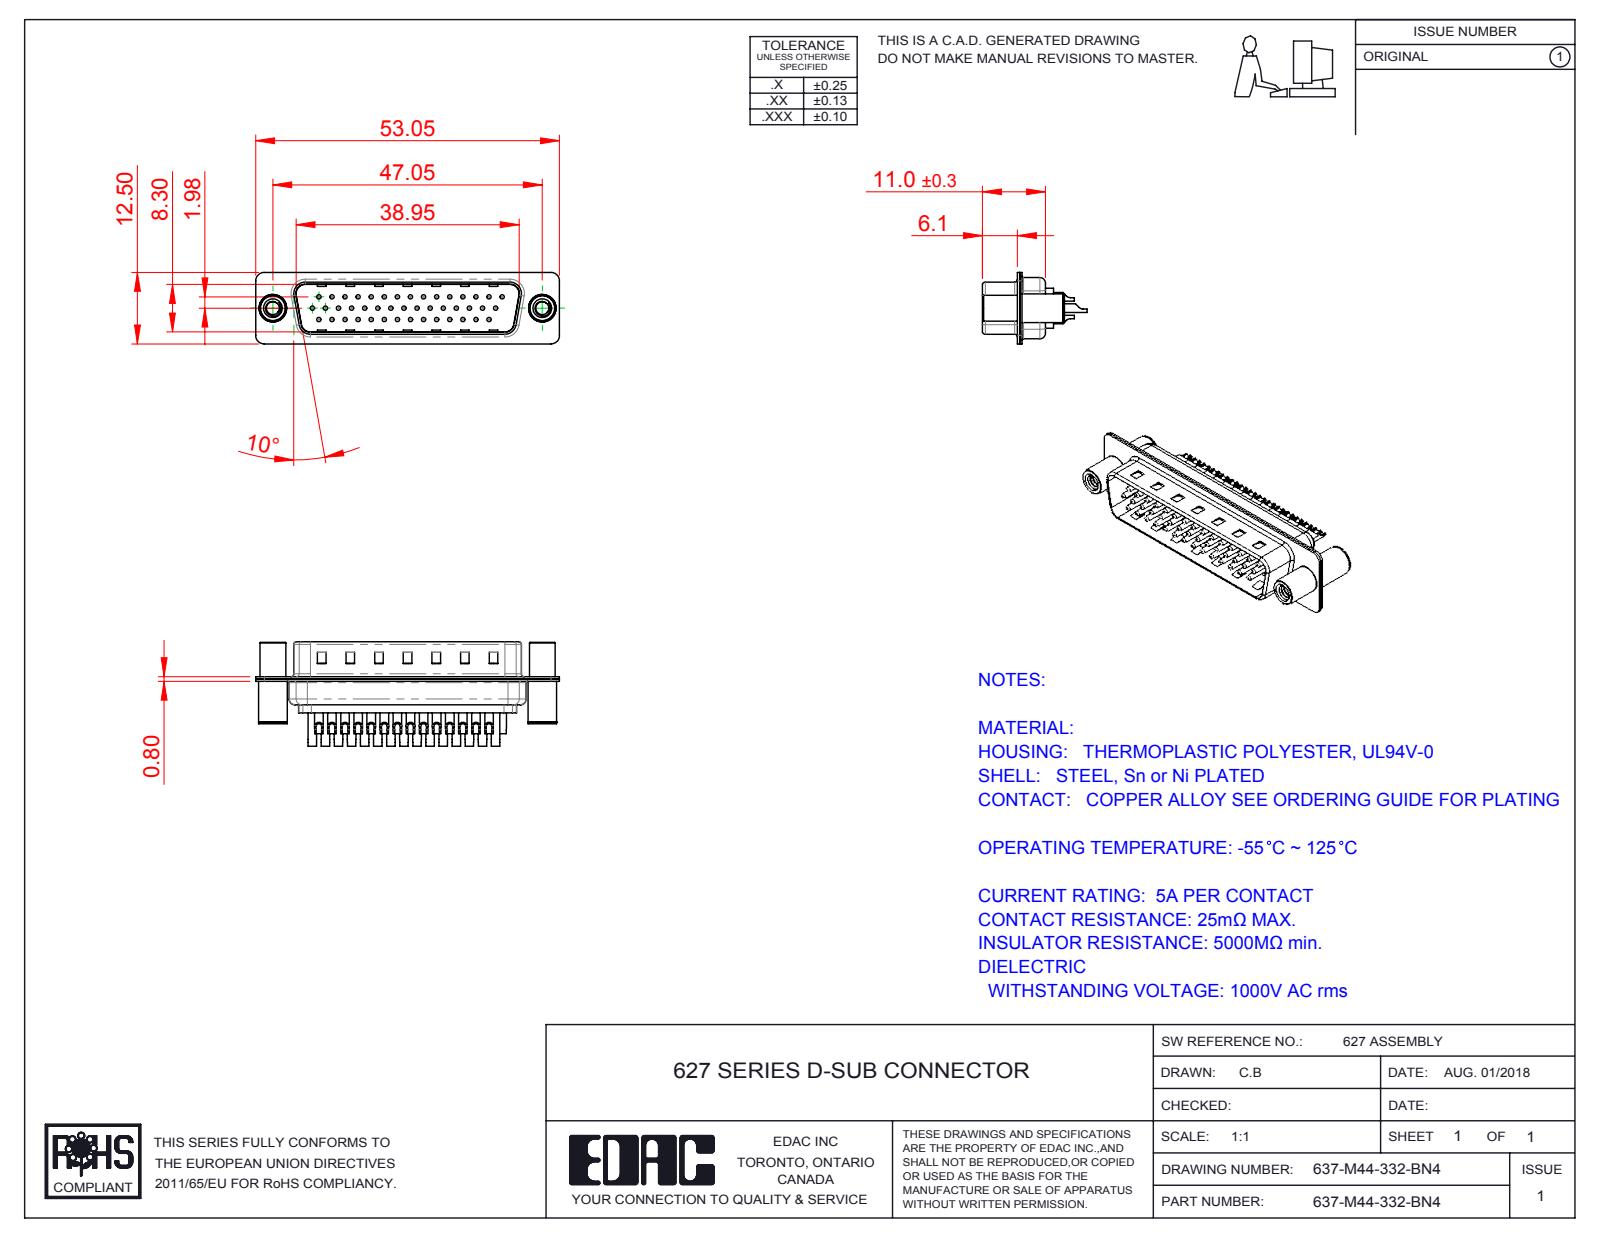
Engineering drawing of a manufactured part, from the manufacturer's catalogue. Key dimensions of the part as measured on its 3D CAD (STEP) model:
Part name (STEP PRODUCT): 637M Contact Row 1_32; 637M 4-40 Threaded Standoff and Board Spacer; 637M Housing_44 Contacts; 637-M44-332-BN4 (+4 more)
STEP written by: SolidWorks 2016 (CONFIG_CONTROL_DESIGN)
Units: millimetres
Bodies: 49 solids, 2090 faces (573 planar, 893 cylindrical, 624 other)
Overall size (bounding box): 53.05 × 18.25 × 12.5
Volume: 3 261 mm³ · Surface area: 9 539 mm²
Round holes (diameter × count): ⌀0.75 ×44, ⌀1 ×44, ⌀1.6 ×44, ⌀2 ×44, ⌀2.26 ×2, ⌀3.26 ×2, ⌀4 ×2, ⌀4.8 ×2
Round bosses / shafts (diameter × count): ⌀1.5 ×44, ⌀2 ×3, ⌀0.75 ×3, ⌀5 ×2, ⌀4.9 ×2, ⌀4.5 ×2
Partial cylindrical surfaces — rounded edges, fillets, slot ends (radius × count): R1.5 ×16, R2 ×12, R0.5 ×8, R1.6 ×8, R1 ×7, R0.25 ×4, R0.6 ×4, R0.65 ×4
Main face-to-face distances: 0.4, 0.8, 9.5, 9.1, 8.7, 9.9, 0.75, 0.35, 1.1, 1.2
Hole centre spacings: 2.28, 3.96, 2.29, 4.57, 8.24, 6.86, 11.43, 14.99
